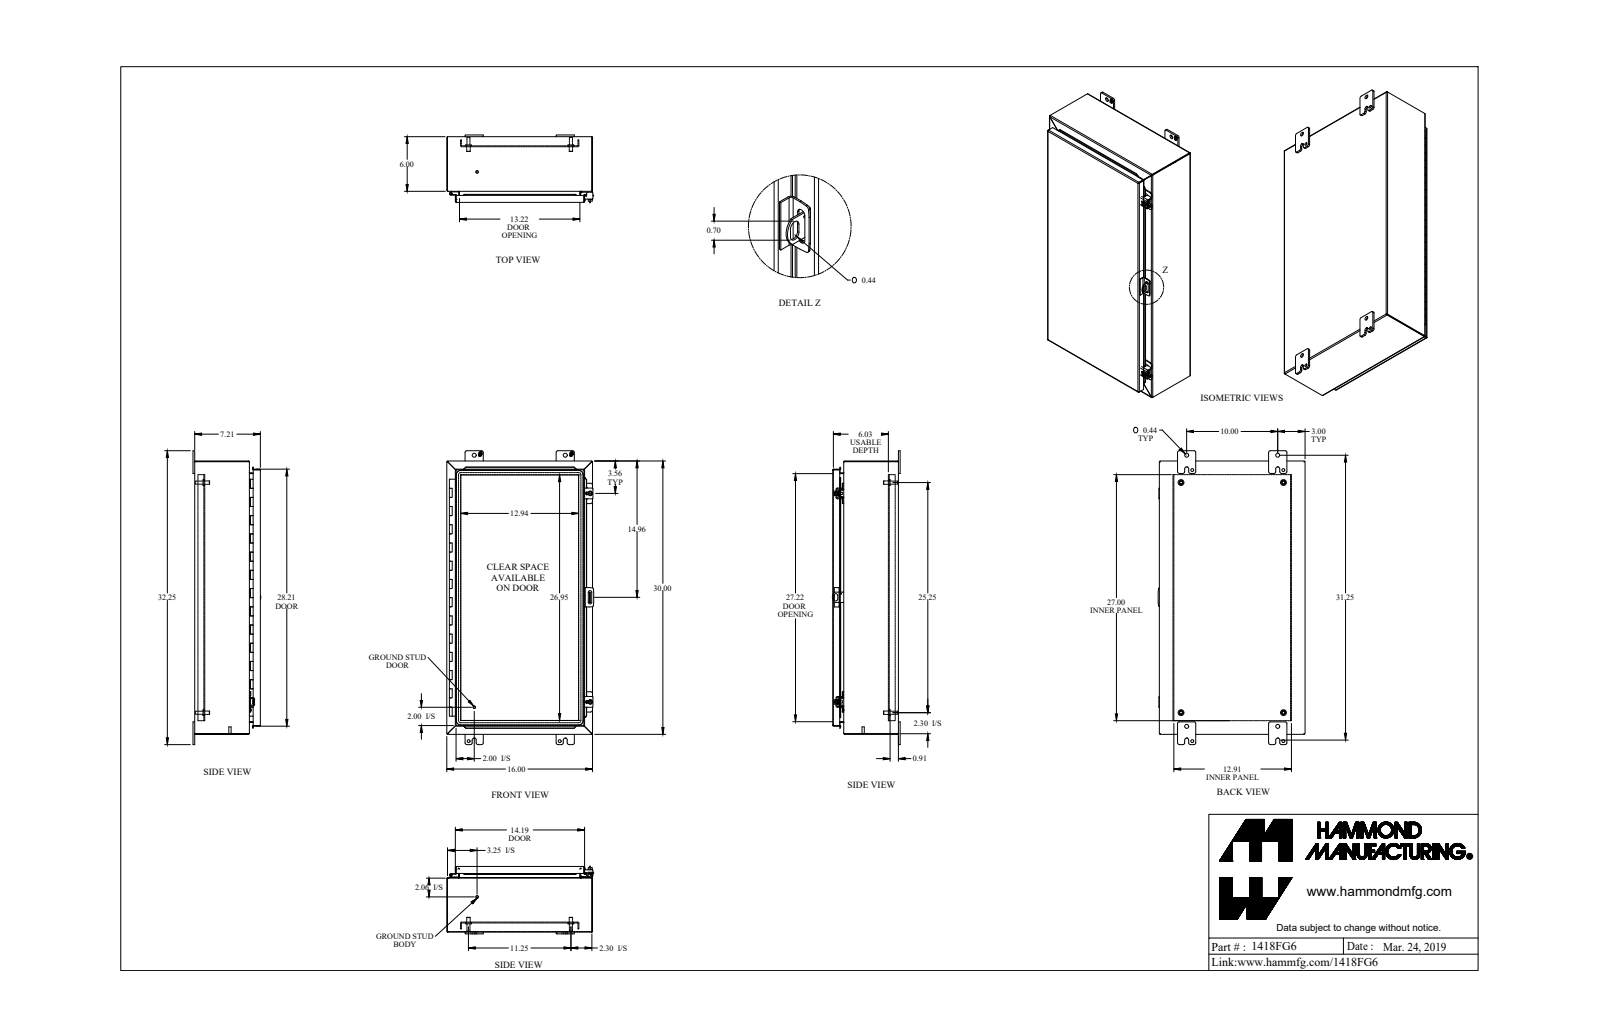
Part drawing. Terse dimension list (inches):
name: 1418FG6
written by: SolidWorks 2019 (AUTOMOTIVE_DESIGN)
unit: in
bodies: 38 solids, 1034 faces (717 planar, 269 cylindrical, 48 other)
size: 32.25 × 16.125 × 7.437
volume: 180.9 in³; area: 4 675 in²
holes: 4× ⌀0.313, 4× ⌀0.437, 4× ⌀0.5, 2× ⌀0.213, 2× ⌀0.265, 2× ⌀0.307, 2× ⌀0.375, 2× ⌀0.445, 1× ⌀0.125, 1× ⌀0.187
bosses: 4× ⌀0.65, 4× ⌀0.375, 4× ⌀0.33, 2× ⌀1, 2× ⌀0.5, 2× ⌀0.39, 2× ⌀0.281, 2× ⌀0.25
rounds: 26× R0.188, 20× R0.036, 20× R0.108, 13× R0.048, 13× R0.143, 8× R0.045, 8× R0.218, 8× R0.25
face distances: 0.072, 7.113, 7.041, 0.937, 7.185, 1.009, 0.095, 15.928, 6.081, 6.009
hole spacings: 1.736, 10, 11.25, 29.75, 31.386, 27.53, 27.643, 27.643
